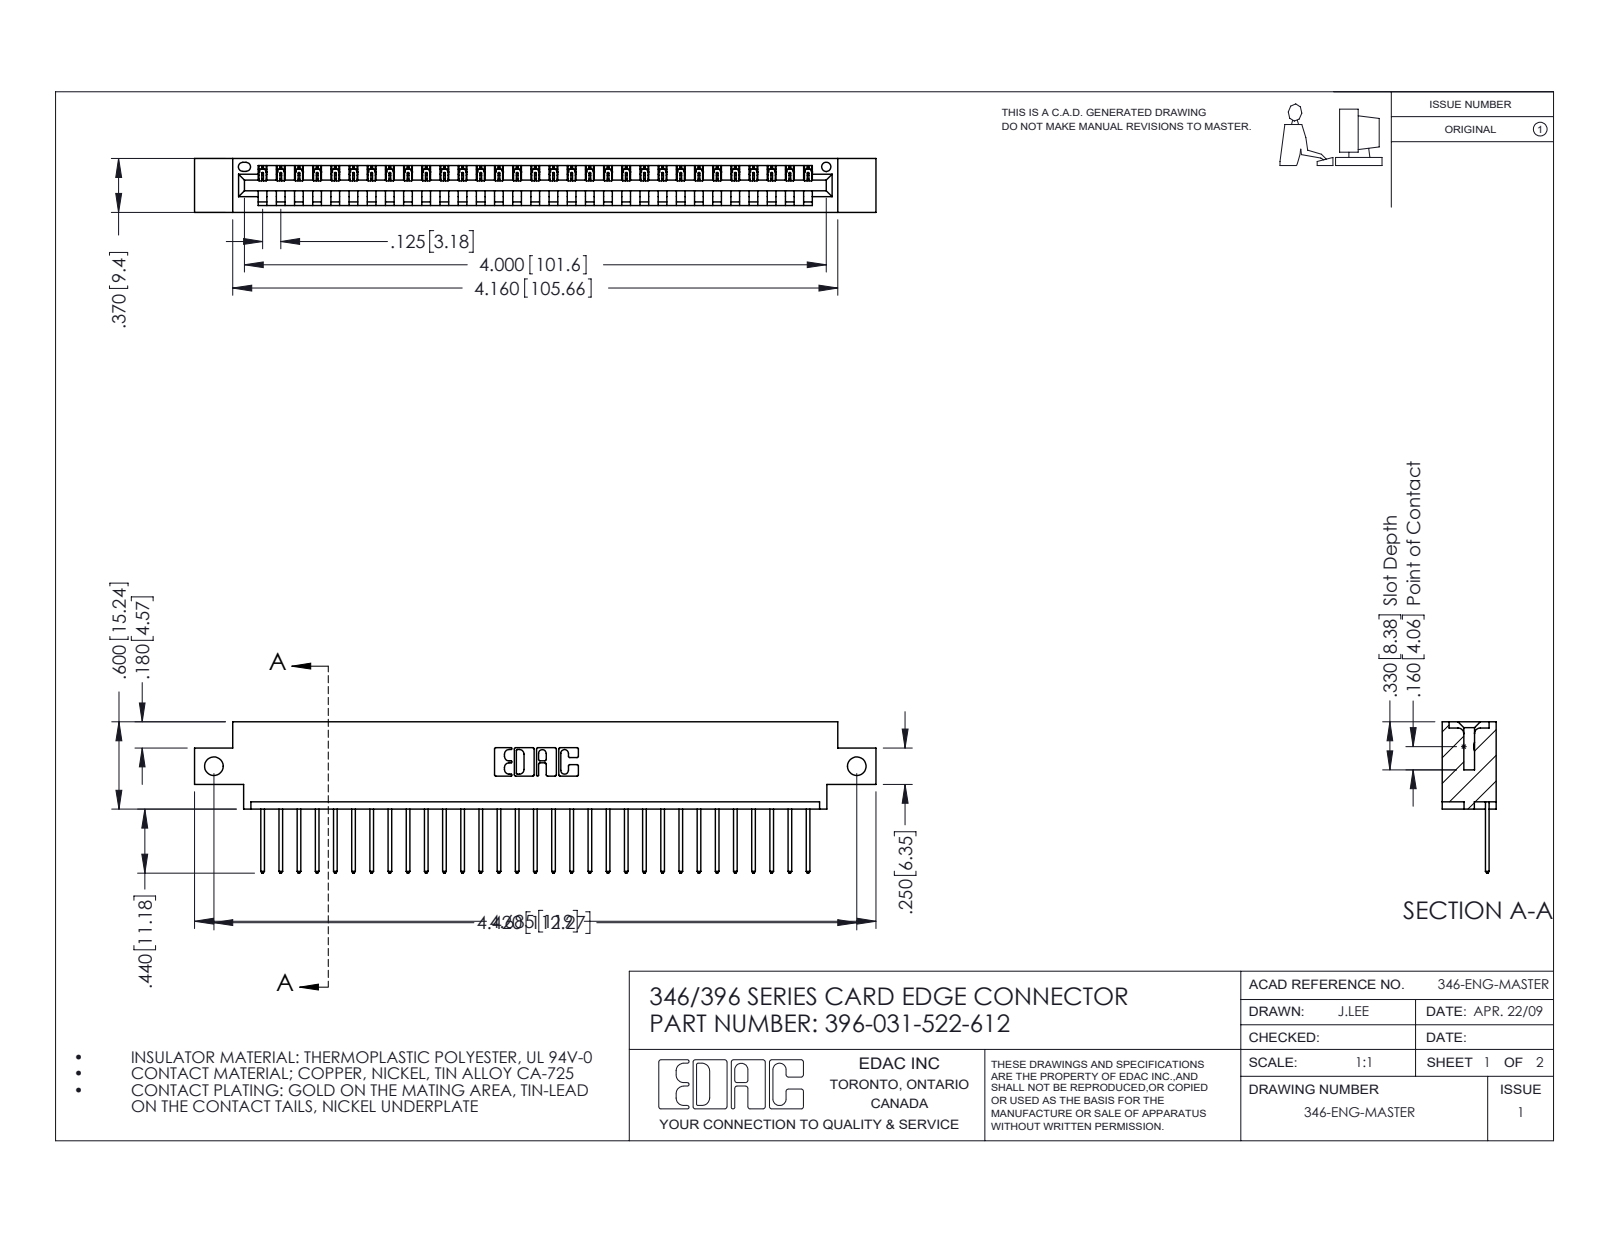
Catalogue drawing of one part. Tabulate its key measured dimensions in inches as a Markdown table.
| quantity | value |
| --- | --- |
| part name | 396-031-522-612; 346 Part_0.170 Offset - Side Mount; 345-292-001_345-293-122 |
| STEP written by | SolidWorks 2016 (CONFIG_CONTROL_DESIGN) |
| units | inches |
| bodies | 32 solids, 1924 faces (1320 planar, 604 cylindrical, 0 other) |
| overall size | 4.685 × 1.04 × 0.37 |
| volume | 0.676 in³ |
| surface area | 21.48 in² |
| round holes (diameter × count) | 0.128 × 2, 0.064 × 1 |
| partial cylindrical surfaces (radius × count) | 0.006 × 62, 0.01 × 62, 0.01 × 22, 0.007 × 6, 0.031 × 6, 0.026 × 3, 0.031 × 2, 0.04 × 2 |
| main face-to-face distances | 0.048, 0.322, 0.37, 0.25, 0.072, 0.298, 0.025, 0.148, 0.222, 0.1 |
| hole center spacings | 4.42 |
